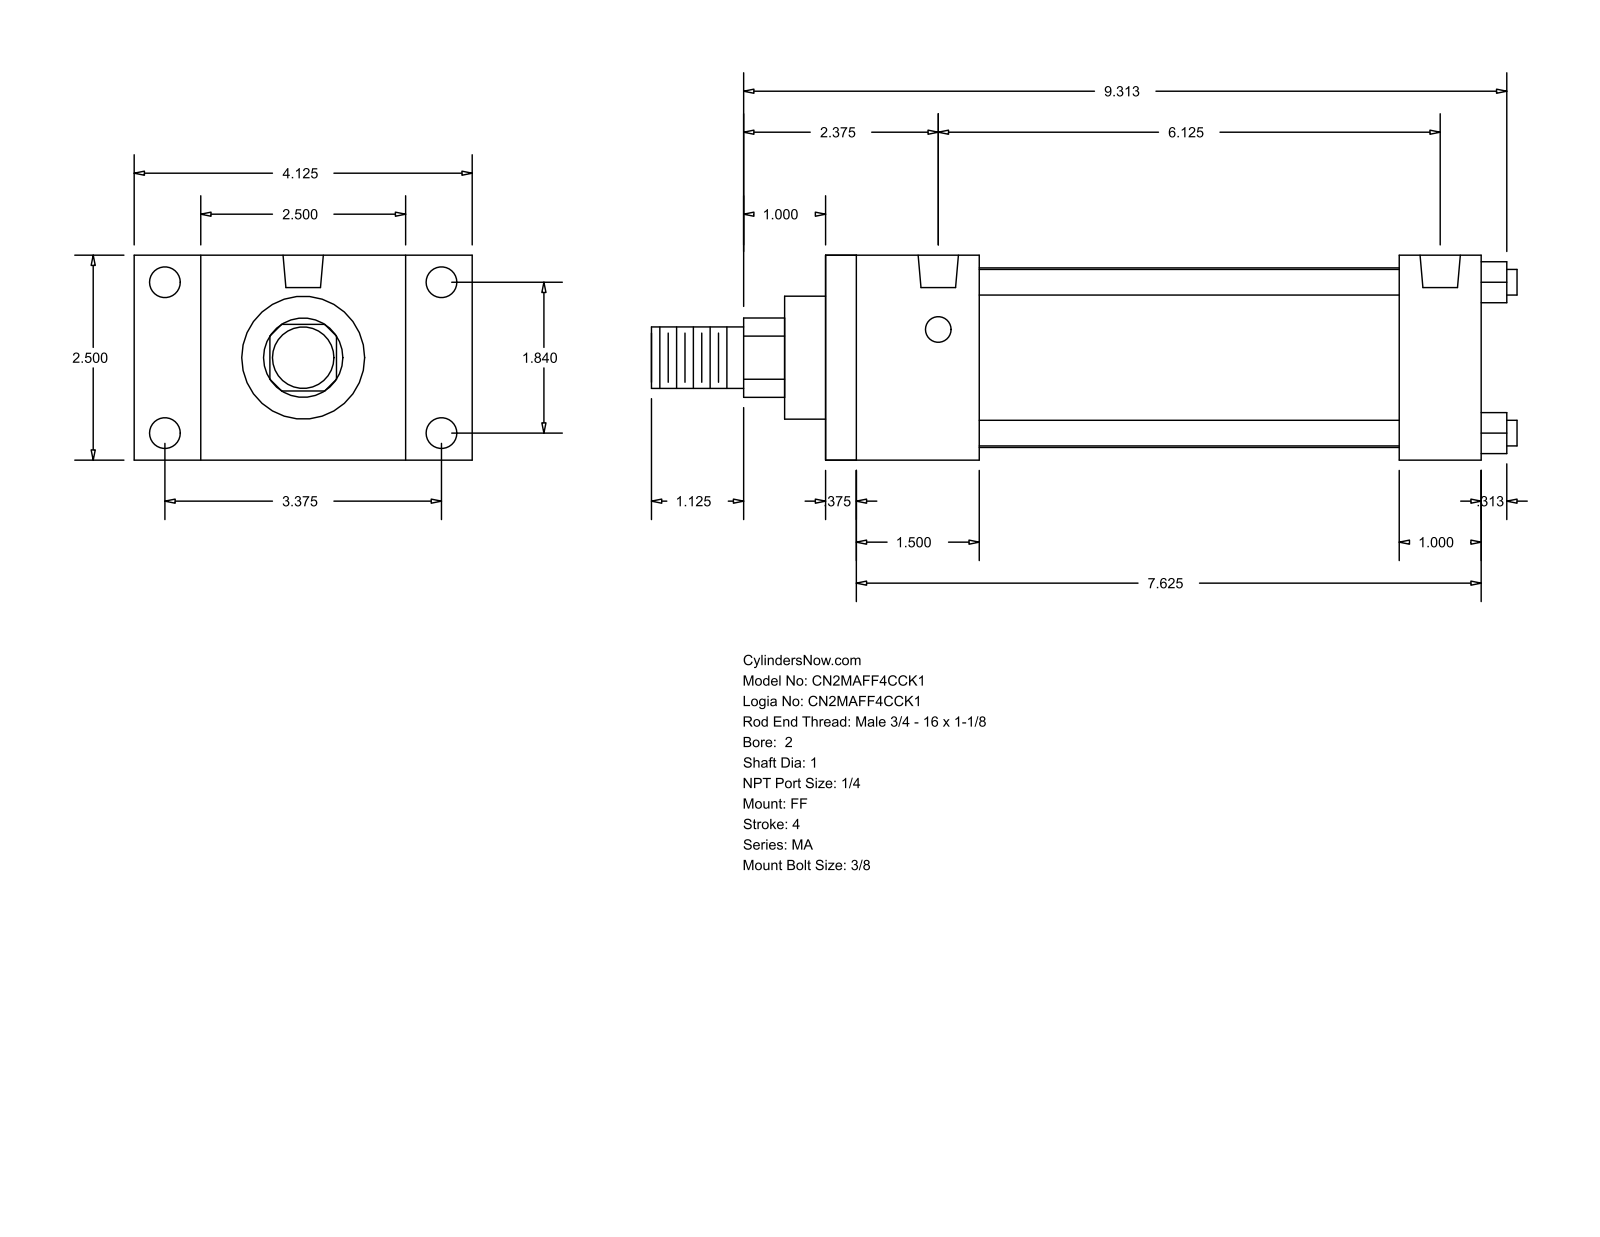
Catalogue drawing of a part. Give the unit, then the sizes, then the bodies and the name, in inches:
Units: inches
Overall size (bounding box): 10.563 × 4.125 × 2.5
Round holes (diameter × count): ⌀0.313 ×4, ⌀0.375 ×4, ⌀0.492 ×2
Round bosses / shafts (diameter × count): ⌀0.313 ×4, ⌀2.19 ×1, ⌀1.5 ×1, ⌀1 ×1, ⌀0.75 ×1
Partial cylindrical surfaces — rounded edges, fillets, slot ends (radius × count): R0.484 ×1
Main face-to-face distances: 2.5, 8, 0.375, 7.625, 1, 0.813, 0.5, 1.875, 7, 1.5
Hole centre spacings: 1.84, 3.375, 3.844, 6.125
Bodies: 0 solids, 92 faces (64 planar, 28 cylindrical, 0 other)
Part name (STEP PRODUCT): MA_FF__0200_1
STEP written by: GSSL Pune (CONFIG_CONTROL_DESIGN)
